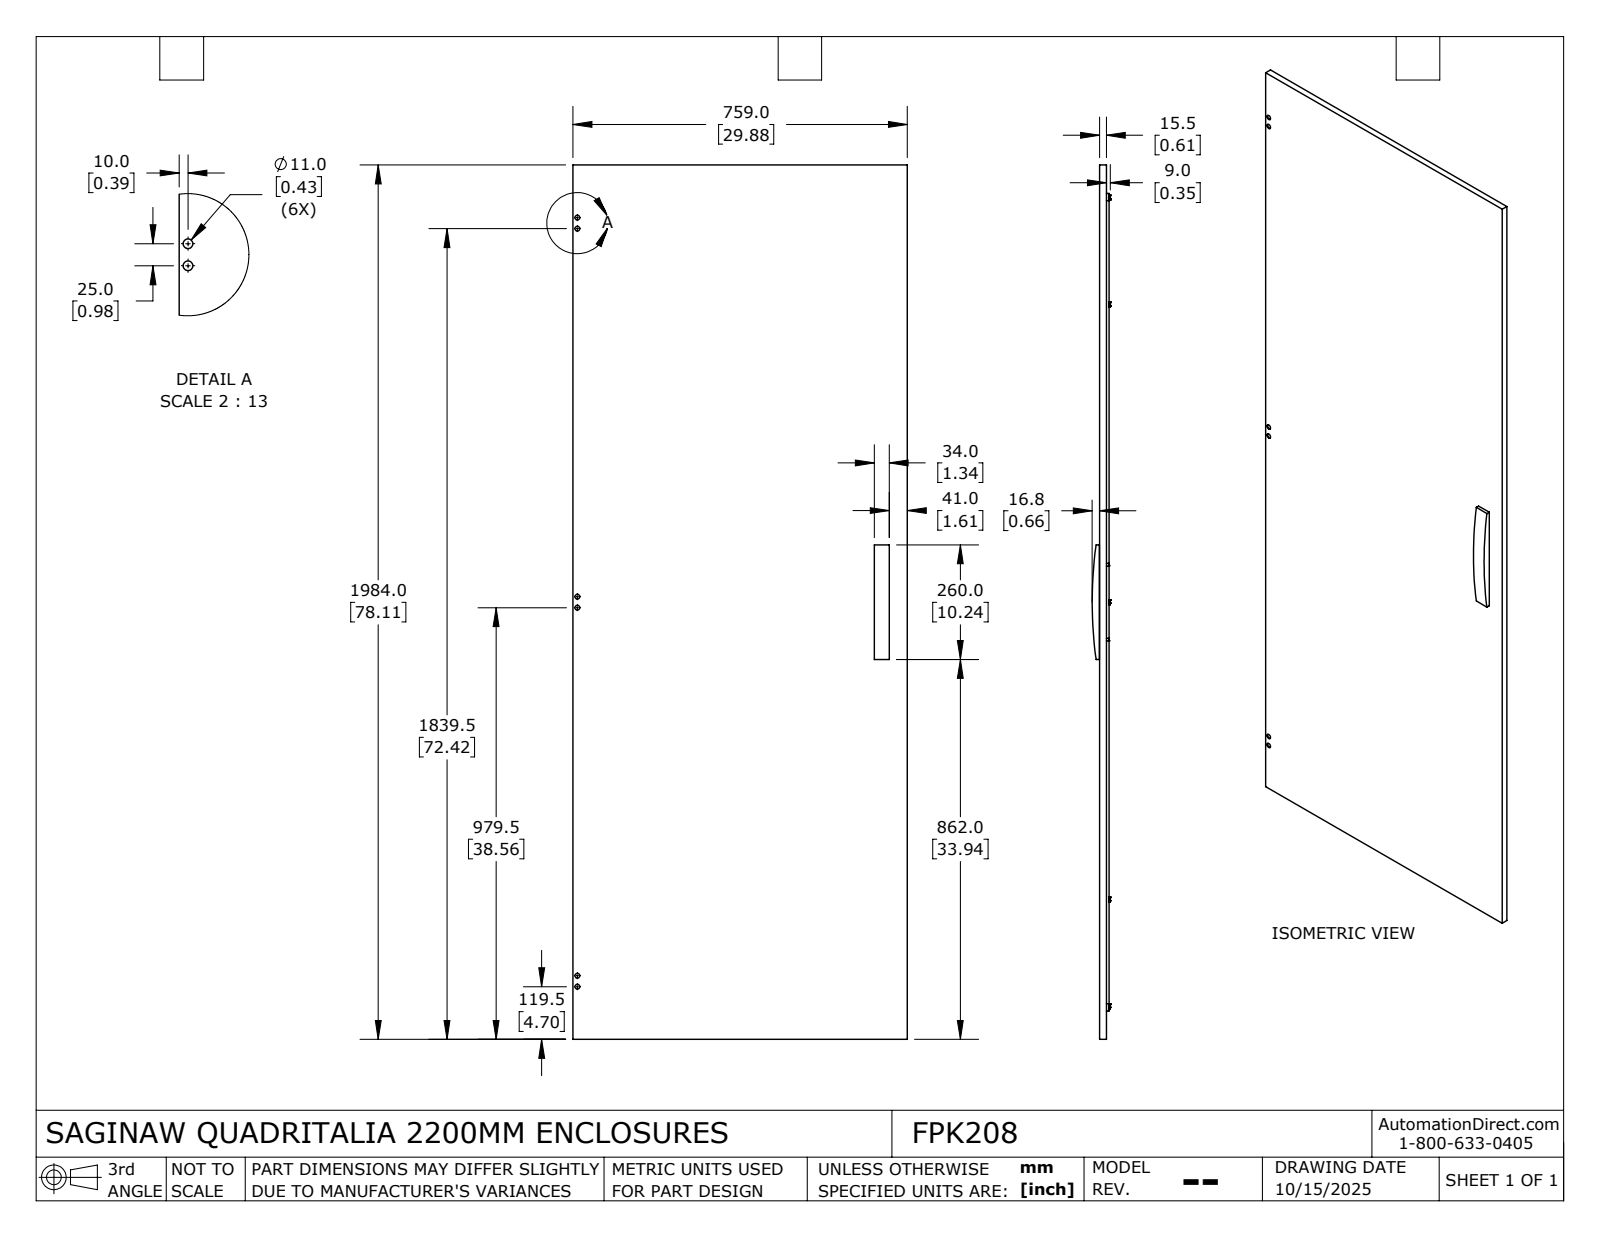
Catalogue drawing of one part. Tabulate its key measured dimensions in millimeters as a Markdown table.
| quantity | value |
| --- | --- |
| part name | FPK208 |
| STEP written by | SolidWorks 2024 (AUTOMOTIVE_DESIGN) |
| units | millimeters |
| bodies | 2 solids, 636 faces (299 planar, 235 cylindrical, 102 other) |
| overall size | 1984 × 759 × 41.32 |
| volume | 4 554 000 mm³ |
| surface area | 3 500 000 mm² |
| round holes (diameter × count) | 4.25 × 144, 9 × 12, 4.92 × 7, 11 × 6, 2.5 × 2, 4.92 × 1 |
| round bosses / shafts (diameter × count) | 7 × 6, 6 × 6, 7.2 × 2 |
| partial cylindrical surfaces (radius × count) | 1 × 8, 5.77 × 8, 7.52 × 4, 962.86 × 1 |
| main face-to-face distances | 1.5, 20, 21.5, 560, 18.5, 757.5, 83, 580, 540, 64.5 |
| hole center spacings | 25, 50, 75, 100, 125, 150, 175, 200 |
